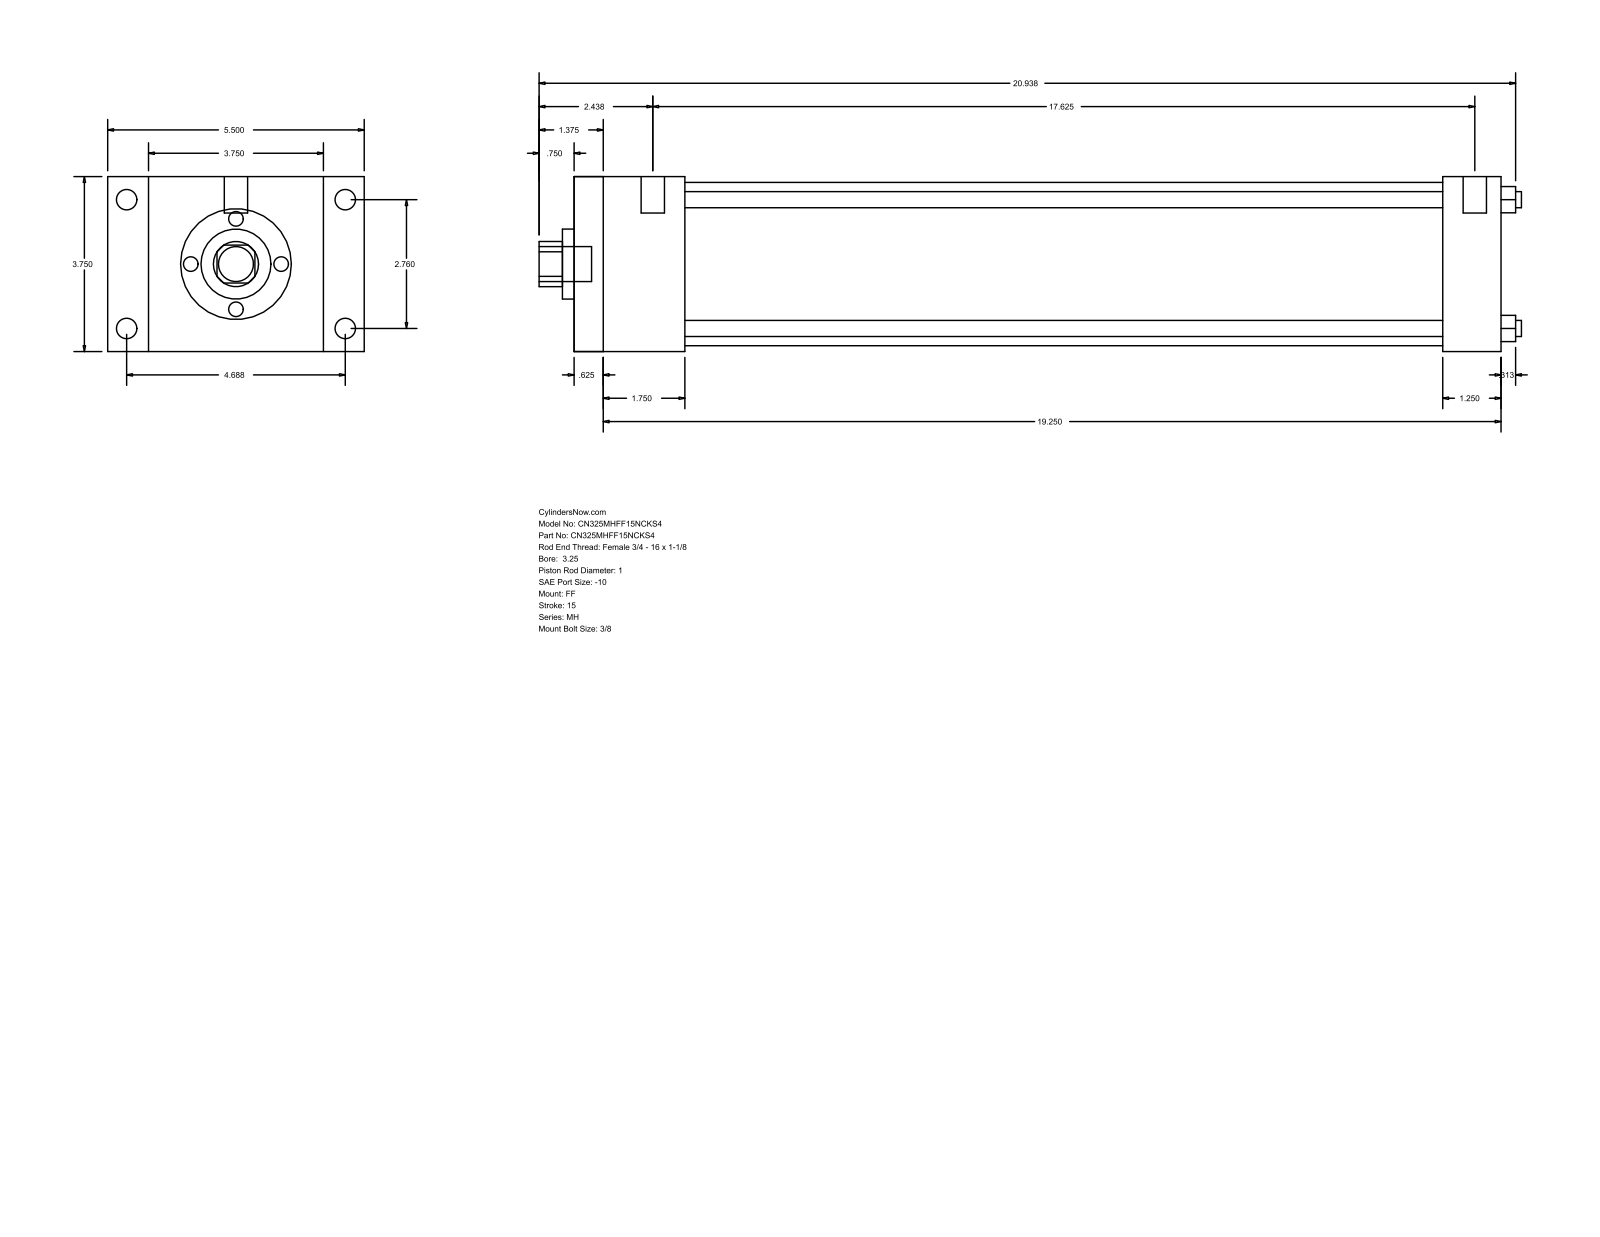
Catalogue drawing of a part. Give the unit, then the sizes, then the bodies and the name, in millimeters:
Units: millimetres
Overall size (bounding box): 534.99 × 139.7 × 95.25
Round holes (diameter × count): ⌀8.76 ×4, ⌀25.4 ×1, ⌀38.1 ×1, ⌀88.9 ×1
Round bosses / shafts (diameter × count): ⌀11.13 ×4, ⌀5.56 ×4, ⌀12.7 ×2, ⌀19.05 ×1
Partial cylindrical surfaces — rounded edges, fillets, slot ends (radius × count): R12.29 ×1
Main face-to-face distances: 95.24, 504.83, 15.87, 488.96, 22.23, 117.47, 473.07, 457.2, 31.76, 60.33
Hole centre spacings: 49.57, 70.1, 99.14
Bodies: 0 solids, 92 faces (64 planar, 28 cylindrical, 0 other)
Part name (STEP PRODUCT): MH_FF__0325_1
STEP written by: GSSL Pune (CONFIG_CONTROL_DESIGN)
